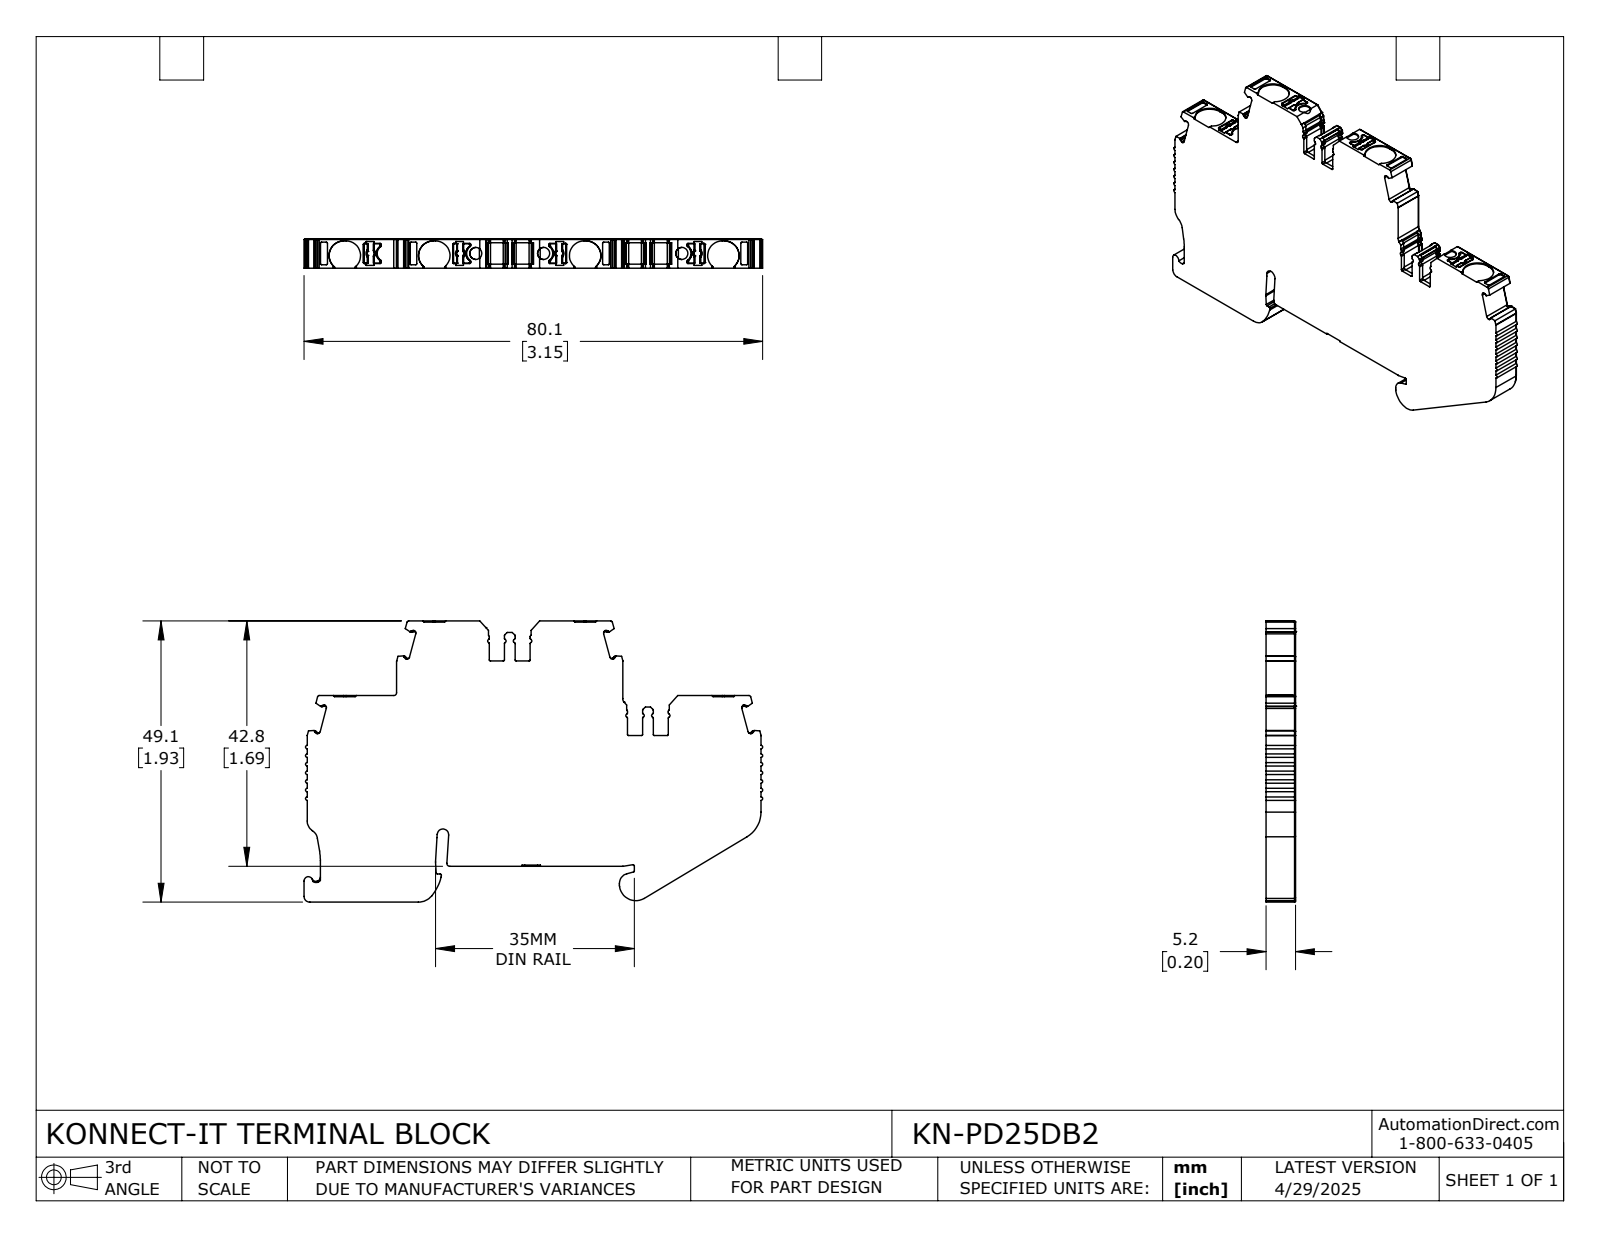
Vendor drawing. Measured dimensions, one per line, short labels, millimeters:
name: KN-PD25DB2
written by: SolidWorks 2024 (CONFIG_CONTROL_DESIGN)
unit: mm
bodies: 1 solid, 977 faces (472 planar, 438 cylindrical, 67 other)
size: 80.09 × 49.09 × 5.15
volume: 14 572 mm³; area: 7 506 mm²
holes: 3× ⌀2.1
rounds: 100× R0.2, 57× R0.3, 41× R0.1, 21× R0.5, 17× R0.4, 16× R0.15, 9× R0.6, 8× R0.16
face distances: 5.15, 13.01, 6.26, 42.62, 29.61, 48.88, 2, 35.87, 12.81, 24.14
hole spacings: 11.84, 24.14, 35.98
